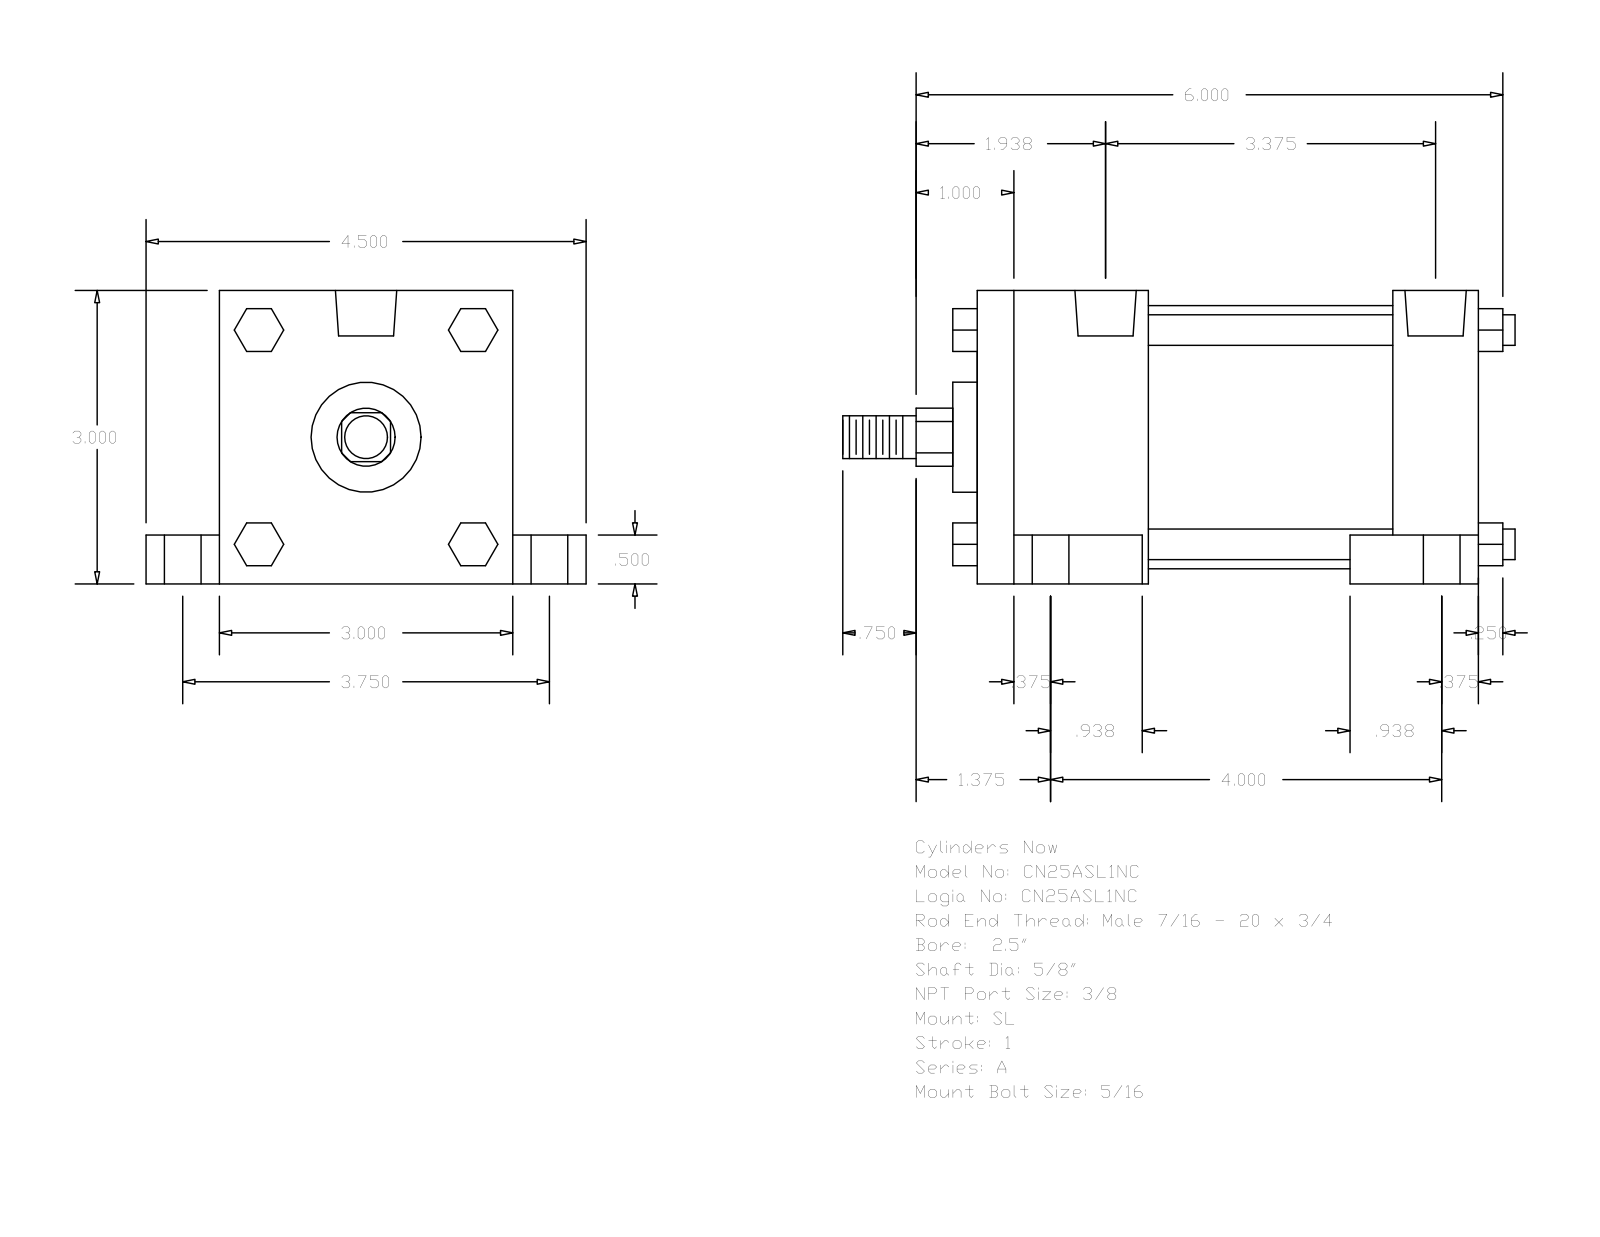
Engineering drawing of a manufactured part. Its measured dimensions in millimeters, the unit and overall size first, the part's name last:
Units: millimetres
Overall size (bounding box): 174.62 × 114.3 × 76.2
Round holes (diameter × count): ⌀5.56 ×4, ⌀9.53 ×4, ⌀15.88 ×4, ⌀15.93 ×2
Round bosses / shafts (diameter × count): ⌀7.94 ×4, ⌀68.33 ×1, ⌀28.57 ×1, ⌀15.88 ×1, ⌀11.11 ×1
Partial cylindrical surfaces — rounded edges, fillets, slot ends (radius × count): R7.54 ×1
Main face-to-face distances: 76.2, 130.17, 63.5, 44.45, 22.22, 85.72, 107.95, 12.7, 19.05, 95.25
Hole centre spacings: 2.38, 47.63, 47.65, 49.09, 49.72, 88.11, 90.49, 95.24
Bodies: 0 solids, 148 faces (112 planar, 36 cylindrical, 0 other)
Part name (STEP PRODUCT): A_SL__0250_0.625
STEP written by: GSSL Pune (CONFIG_CONTROL_DESIGN)
